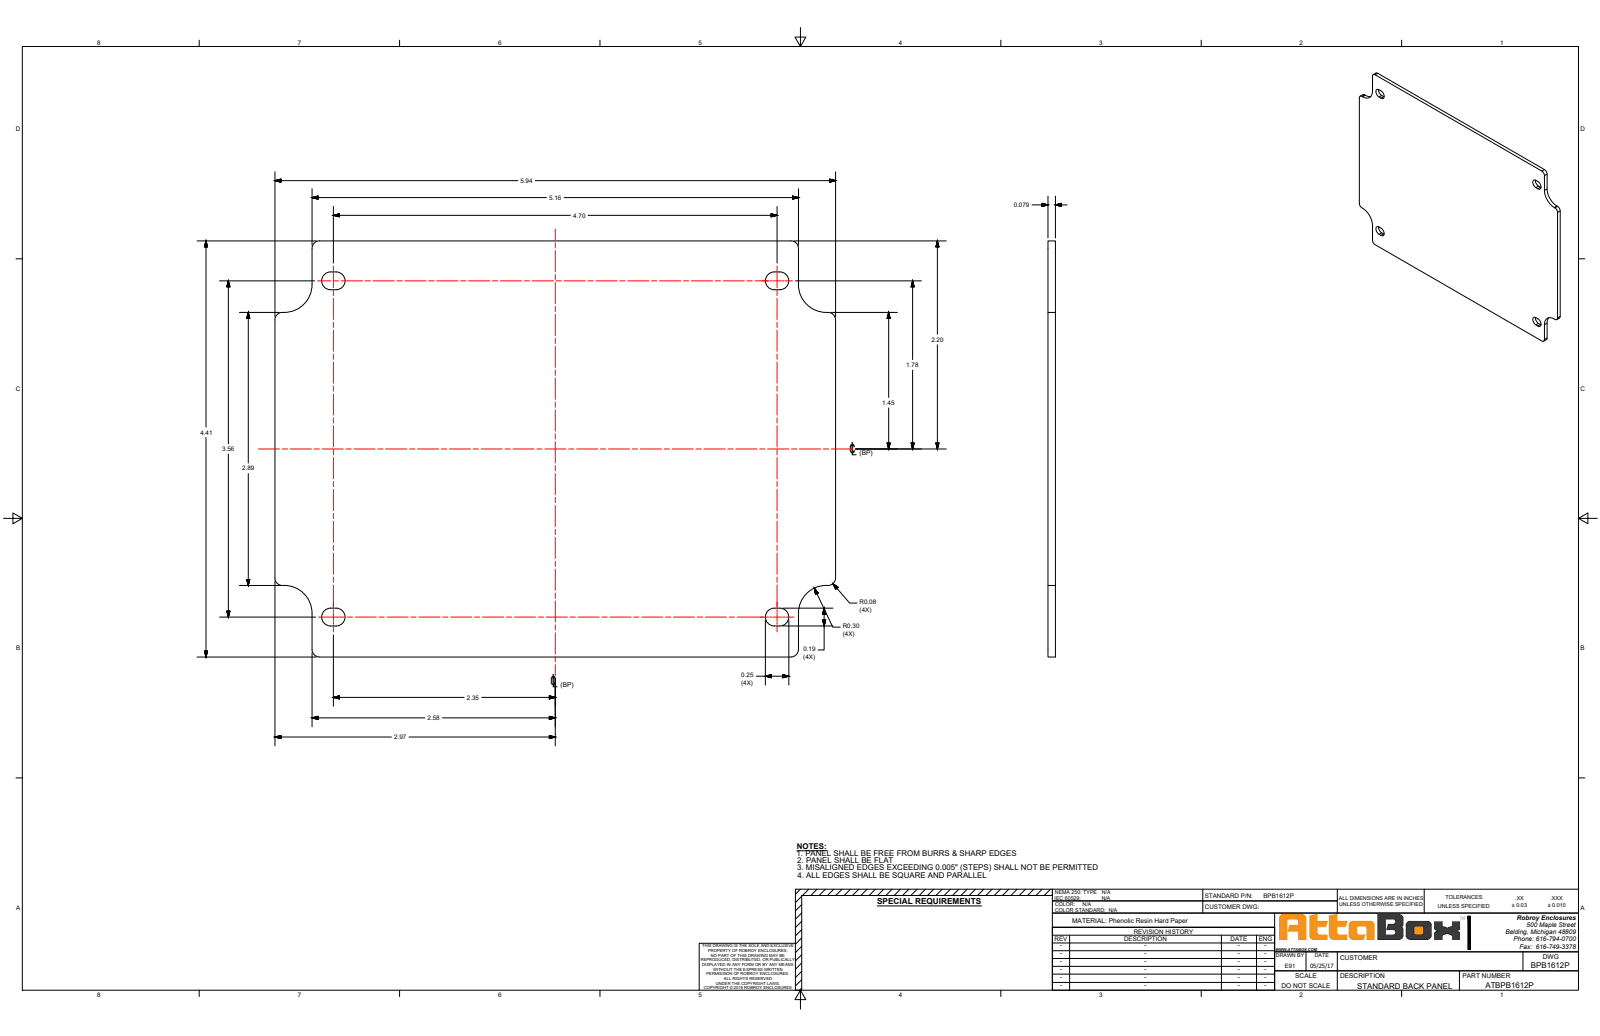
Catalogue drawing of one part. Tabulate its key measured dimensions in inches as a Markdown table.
| quantity | value |
| --- | --- |
| part name | BPB1612P |
| STEP written by | SolidWorks 2018 (AUTOMOTIVE_DESIGN) |
| units | inches |
| bodies | 1 solid, 42 faces (22 planar, 20 cylindrical, 0 other) |
| overall size | 5.945 × 4.409 × 0.079 |
| volume | 1.963 in³ |
| surface area | 51.65 in² |
| partial cylindrical surfaces (radius × count) | 0.079 × 8, 0.094 × 8, 0.295 × 4 |
| main face-to-face distances | 0.079, 4.409, 5.945, 0.394, 5.551, 5.157, 0.329, 0.518, 3.892, 4.081 |
